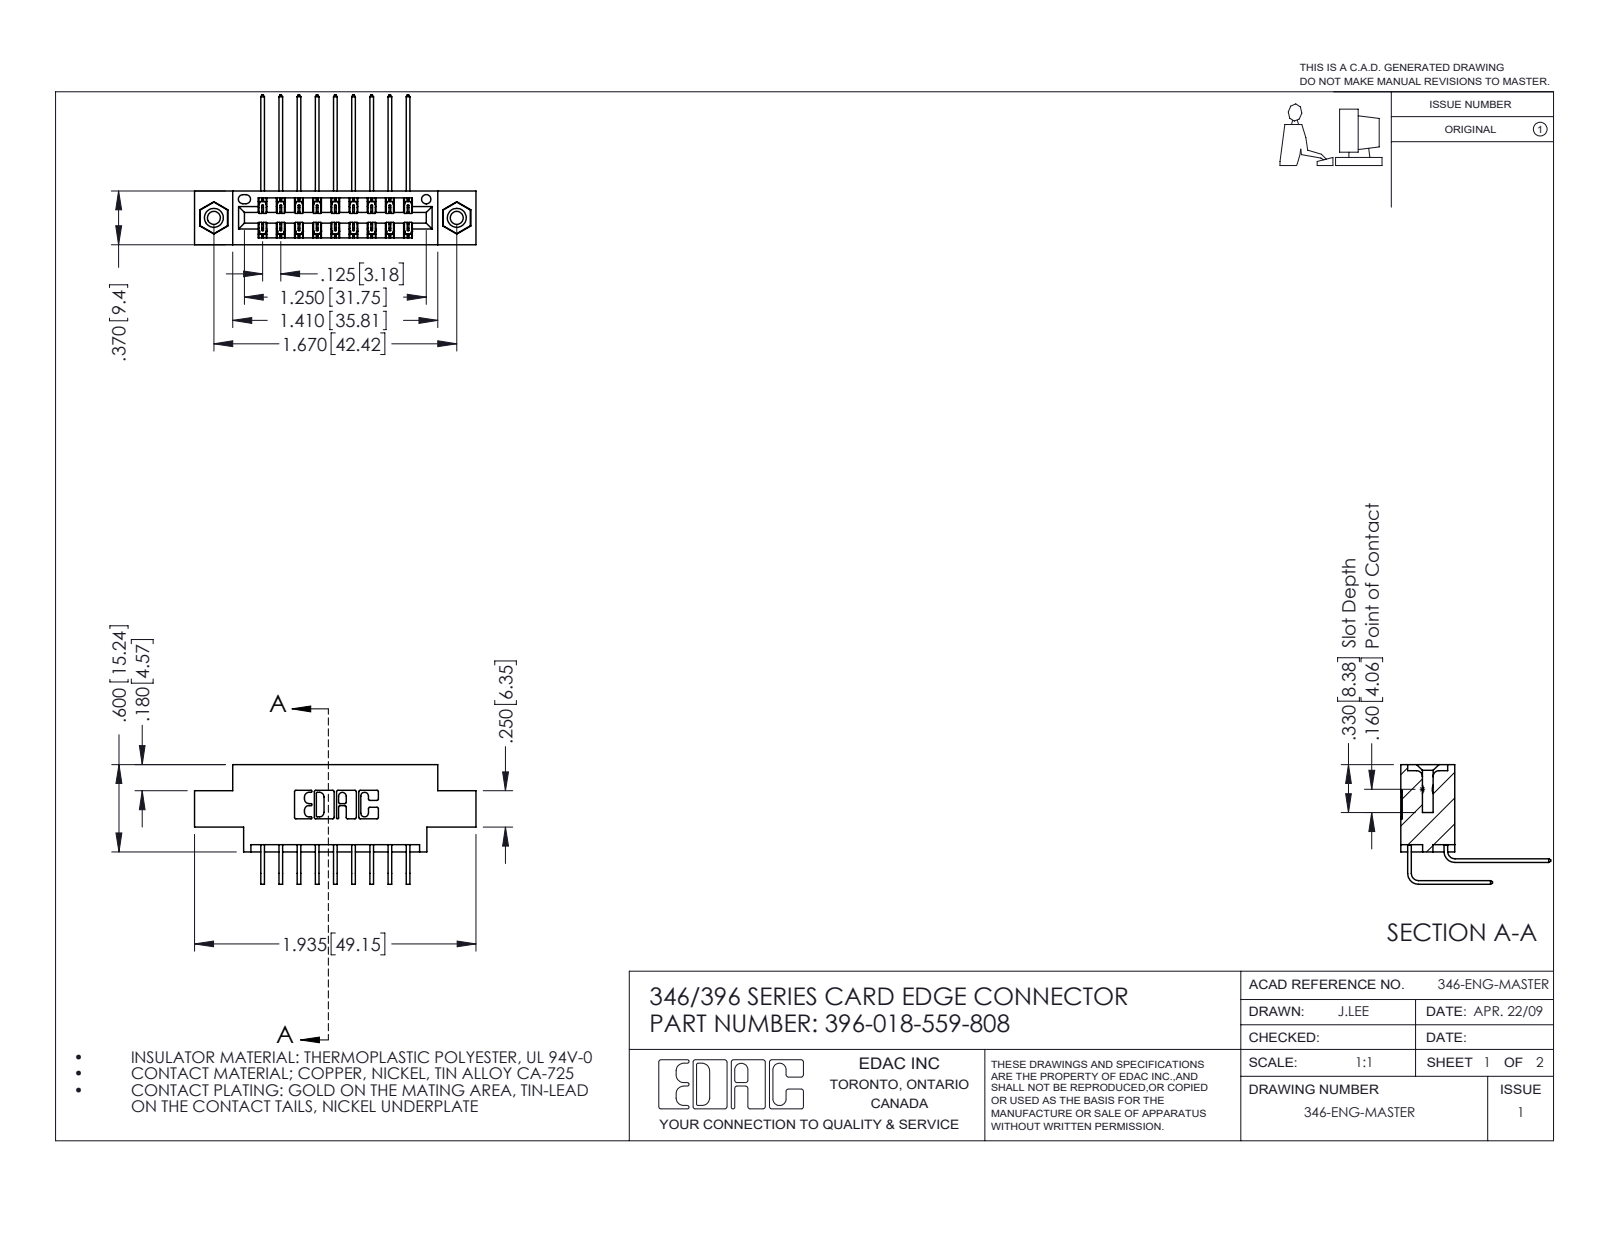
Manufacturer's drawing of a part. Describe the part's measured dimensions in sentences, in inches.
The part is named "396-018-559-808; 345-292-001_558 559 Tail - 1; 345-250-001_345-250-003-102; 346 Part_0.170 Offset - 0.156 Dia-TI (+1 more)". Its 3-D file was written by "SolidWorks 2016 (CONFIG_CONTROL_DESIGN)". It is 21 solids with 1158 faces: 778 planar, 364 cylindrical and 16 other. Overall it measures 1.935 by 1.03 by 0.823 inches. Its volume is 0.273 cubic inches and its surface area 9.821 square inches. Round holes: 2 of diameter 0.089, 2 of diameter 0.125, 2 of diameter 0.156, 1 of diameter 0.064. Round bosses or shafts: 2 of diameter 0.155. Partial cylindrical surfaces (rounded edges, fillets, slot ends): 27 of radius 0.006, 22 of radius 0.01, 6 of radius 0.007, 6 of radius 0.031, 3 of radius 0.026, 2 of radius 0.014, 2 of radius 0.022, 2 of radius 0.024. The main face-to-face distances are 0.25, 0.048, 0.37, 0.322, 0.025, 0.072, 0.298, 0.222, 0.148, 0.125. The hole center spacings are 0.246, 1.465, 1.67.
